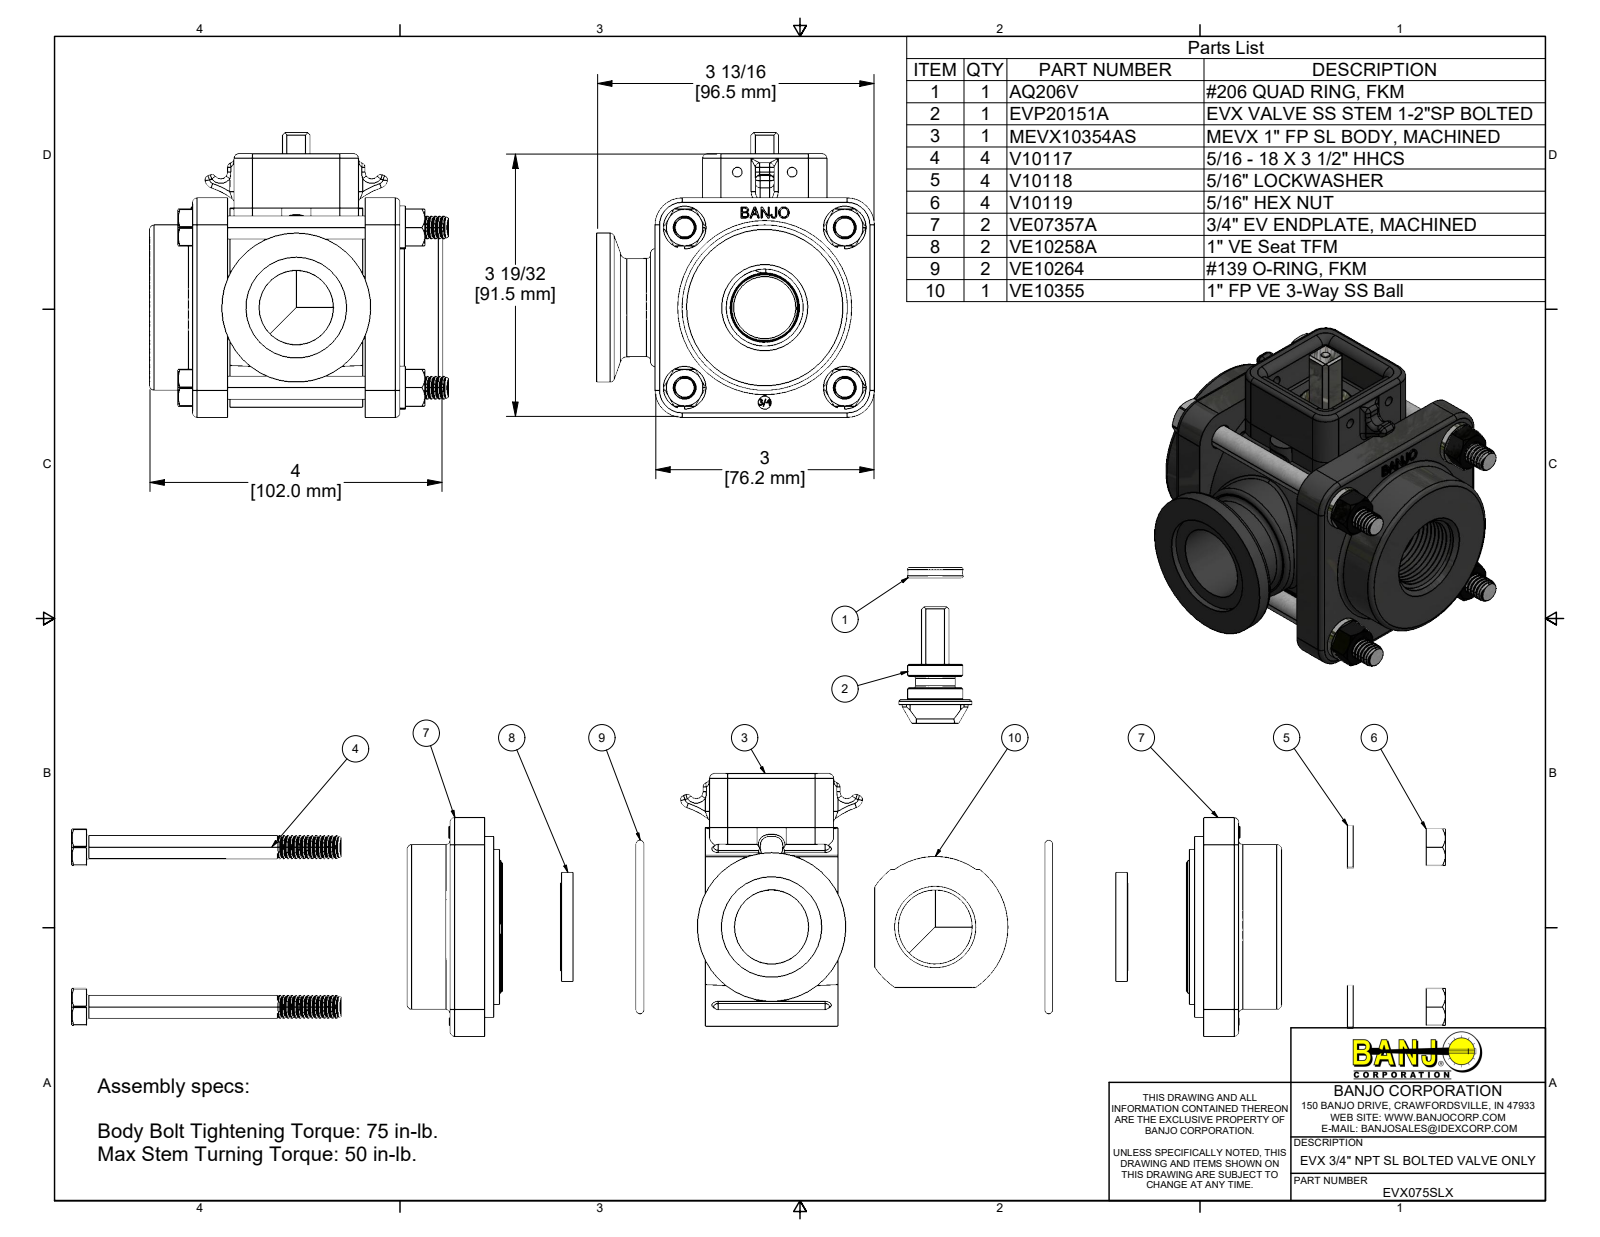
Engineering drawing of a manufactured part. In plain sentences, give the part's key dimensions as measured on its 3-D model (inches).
The part is named "EVX075SLX; MEVX10354AS; MEVX10354ASX; VE10355 (+8 more)". Its 3-D file was written by "Autodesk Inventor 2019 (AUTOMOTIVE_DESIGN)". It is 22 solids with 1599 faces: 374 planar, 532 cylindrical and 693 other. Overall it measures 30.214 by 3.893 by 3.8 inches. Its volume is 22.75 cubic inches and its surface area 502.3 square inches. Round holes: 4 of diameter 0.252, 4 of diameter 0.322, 4 of diameter 0.35, 3 of diameter 1.02, 2 of diameter 0.135, 1 of diameter 0.18, 1 of diameter 0.76, 1 of diameter 1.38, 1 of diameter 1.5, 1 of diameter 2.12, 1 of diameter 2.375, 1 of diameter 2.5. Round bosses or shafts: 60 of diameter 0.268, 4 of diameter 0.583, 4 of diameter 0.313, 1 of diameter 2.725, 1 of diameter 2.48, 1 of diameter 2.26, 1 of diameter 2.124, 1 of diameter 2.04. Partial cylindrical surfaces (rounded edges, fillets, slot ends): 58 of radius 0.06, 12 of radius 0.03, 8 of radius 0.134, 6 of radius 0.125, 4 of radius 0.21, 4 of radius 0.25, 4 of radius 0.284, 4 of radius 0.37. The main face-to-face distances are 0.475, 2.36, 2.95, 0.59, 1.065, 3.425, 3, 2.835, 1.885, 0.125. The hole center spacings are 1.55, 2.192, 1.046, 1.115, 1.891, 2.635, 3.1, 3.176.
